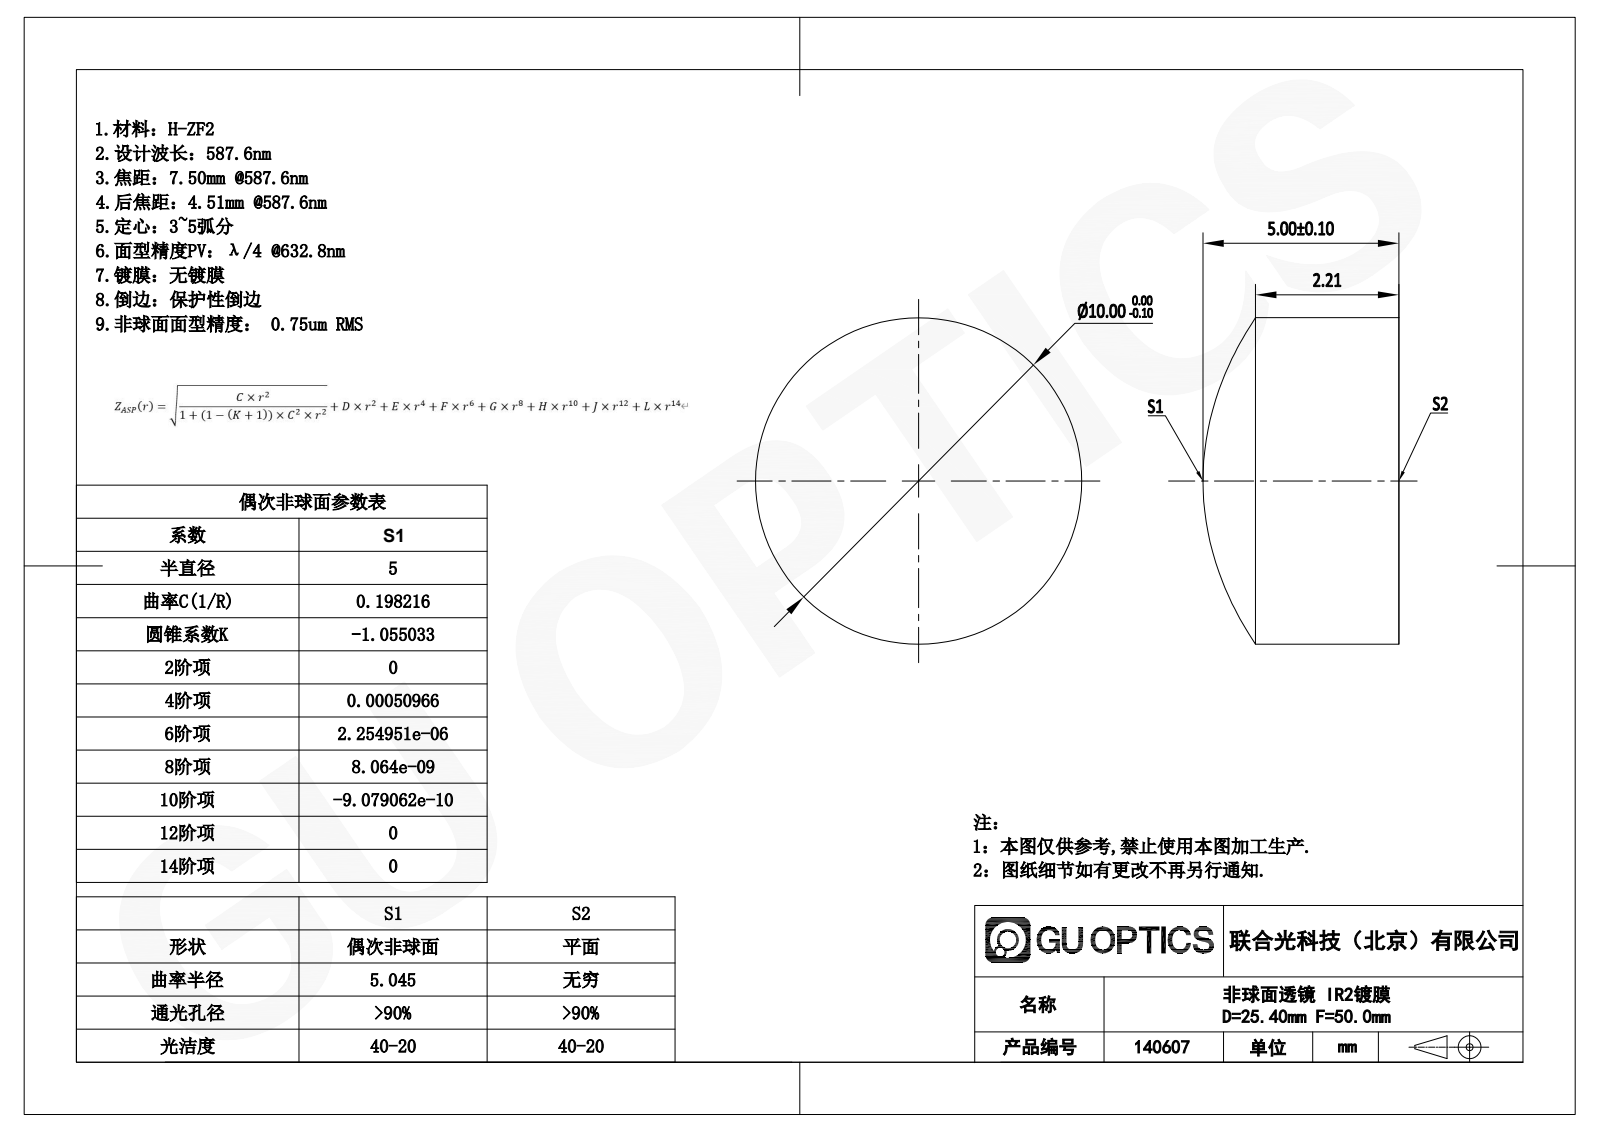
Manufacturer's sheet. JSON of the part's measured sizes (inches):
{"part_name": "surfaces 1,2.stp; GLA11-010-7.5; GLA11-010-7.5.stp", "step_written_by": "SolidWorks 2023 (CONFIG_CONTROL_DESIGN)", "units": "inches", "bodies": {"solids": 1, "faces": 5, "planar": 1, "cylindrical": 2, "other": 2}, "overall_size": [0.394, 0.394, 0.197], "volume_in3": 0.018, "surface_area_in2": 0.386, "round_bosses_or_shafts": [[0.394, 1]]}
